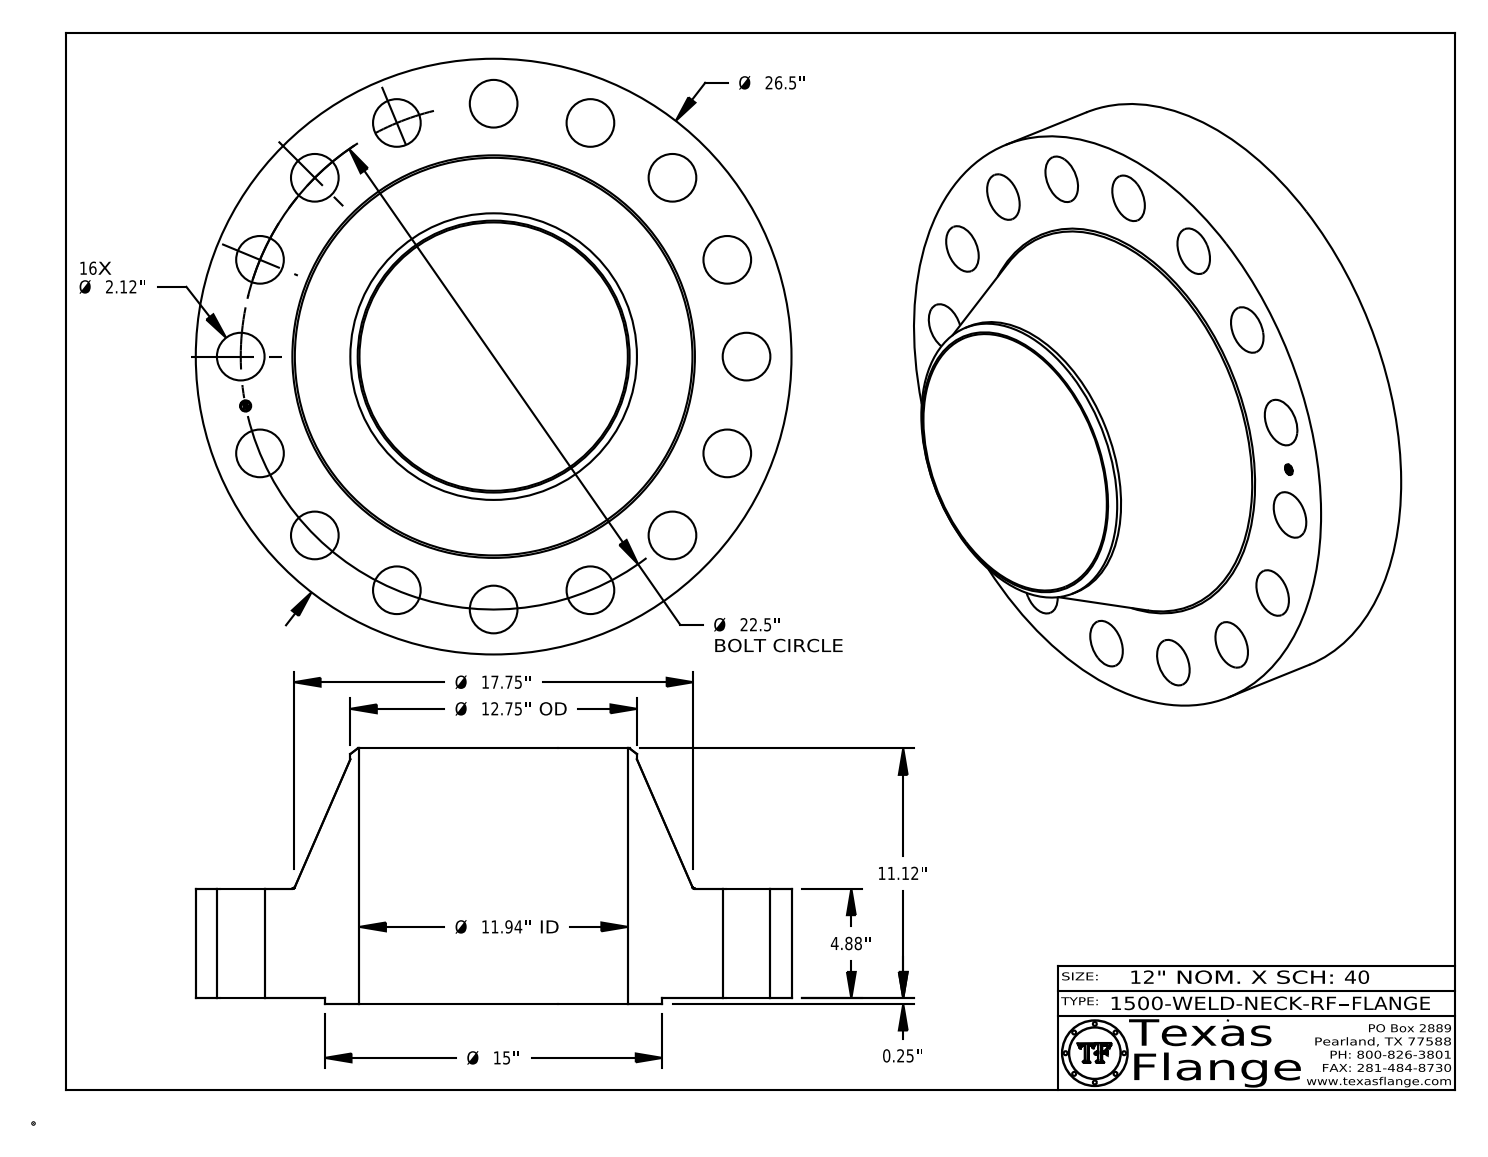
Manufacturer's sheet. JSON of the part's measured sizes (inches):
{"part_name": "1500-WELD-NECK-RF", "step_written_by": "CATIA V5 STEP AP214 (AUTOMOTIVE_DESIGN)", "units": "inches", "bodies": {"solids": 1, "faces": 435, "planar": 369, "cylindrical": 60, "other": 6}, "overall_size": [26.5, 26.5, 11.37], "volume_in3": 2308, "surface_area_in2": 2323, "round_holes": [[2.12, 16], [0.495, 1], [11.938, 1]], "round_bosses_or_shafts": [[0.03, 8], [26.5, 1], [15, 1], [12.75, 1], [0.39, 1]], "face_to_face_distances": [4.88, 0.25, 5.13, 11.37, 11.12, 6.24, 5.115, 4.865, 0.015, 6.255], "hole_center_spacings": [12.5, 20.787, 22.068, 11.25, 8.611, 15.91, 4.389, 4.39]}
